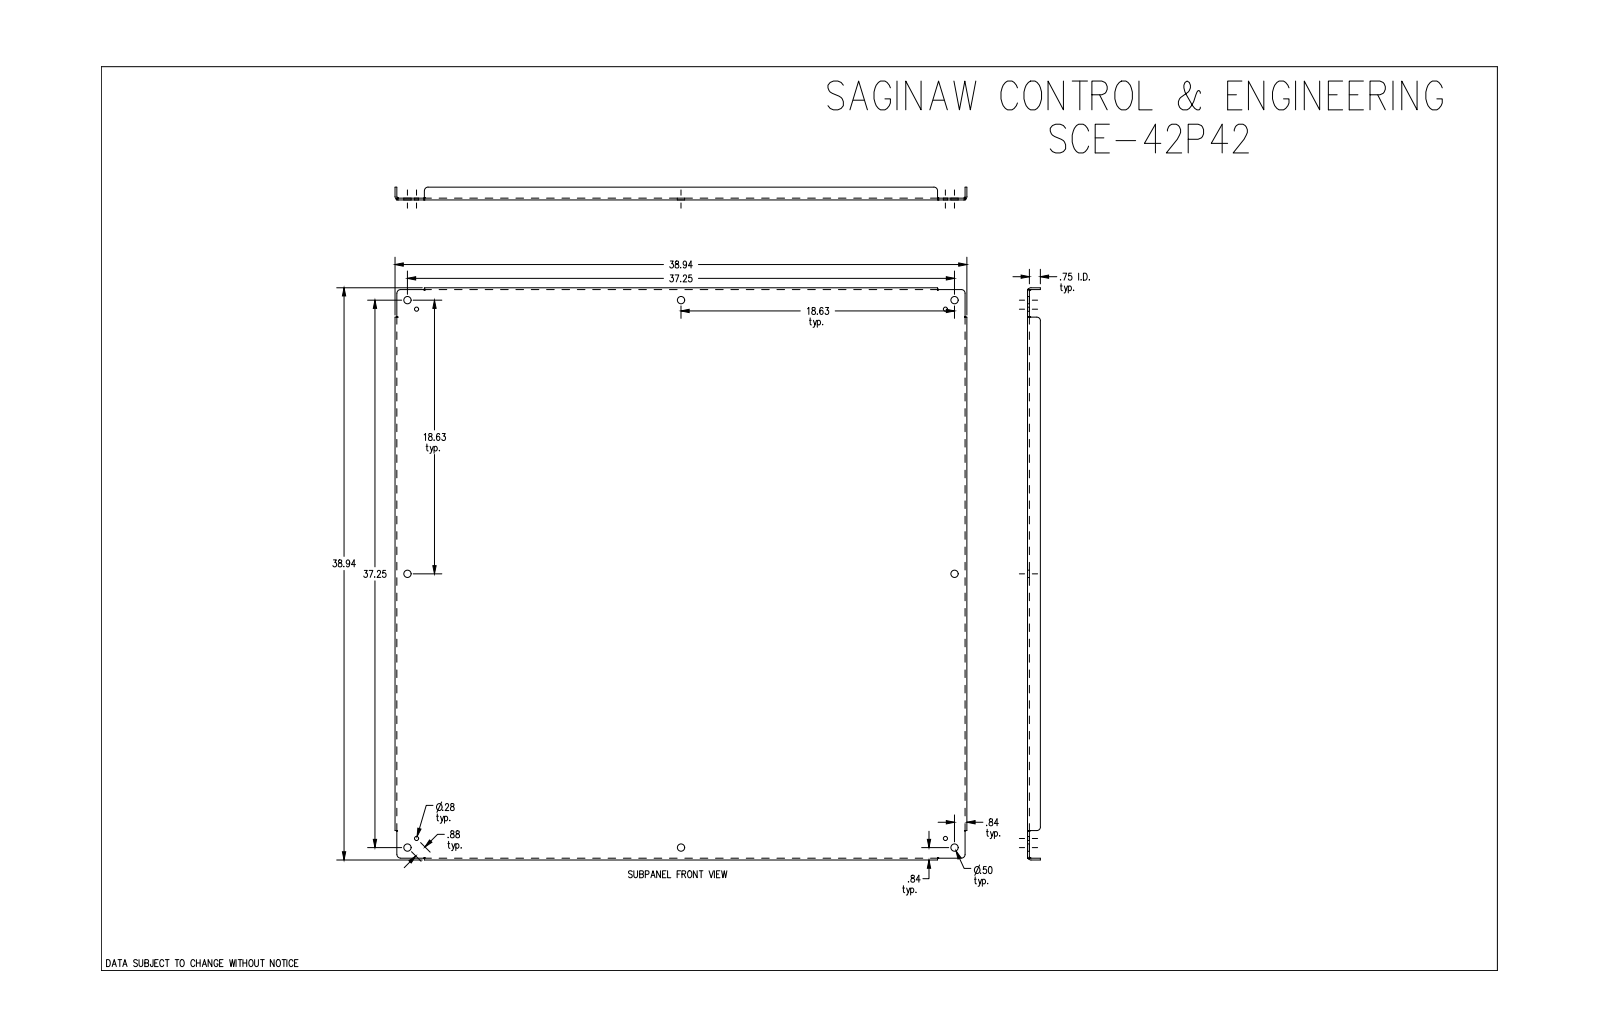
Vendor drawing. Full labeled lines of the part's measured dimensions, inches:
Part name (STEP PRODUCT): SCE-42P42
STEP written by: SolidWorks 2019 (CONFIG_CONTROL_DESIGN)
Units: inches
Bodies: 1 solid, 86 faces (30 planar, 32 cylindrical, 24 other)
Overall size (bounding box): 38.938 × 38.938 × 0.875
Volume: 200.8 in³ · Surface area: 3 235 in²
Round holes (diameter × count): ⌀0.5 ×8, ⌀0.281 ×4
Partial cylindrical surfaces — rounded edges, fillets, slot ends (radius × count): R0.25 ×8, R0.112 ×4, R0.237 ×4
Main face-to-face distances: 0.125, 0.125, 38.813, 38.687, 38.938, 0.75, 0.875, 2, 36.938, 1.875
Hole centre spacings: 18.017, 18.625, 36.636, 40.817, 41.646, 37.25, 0.875, 26.339
